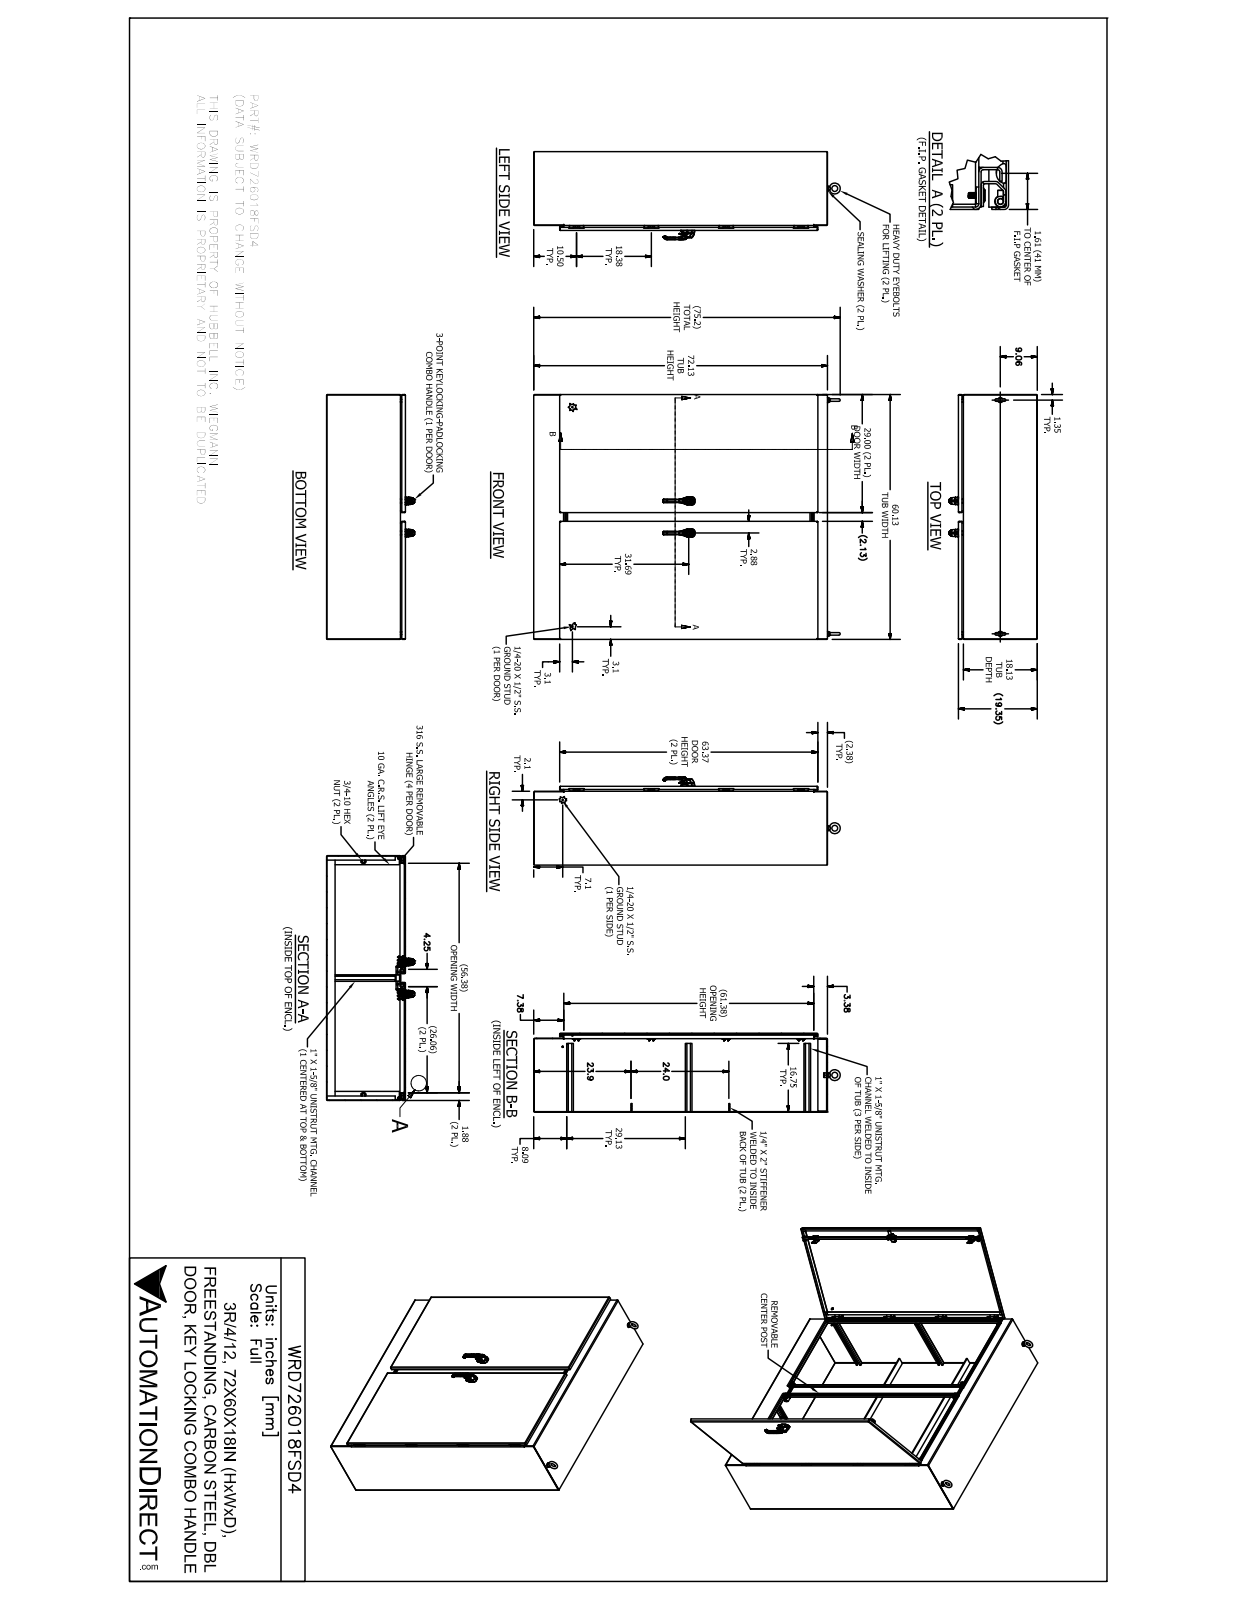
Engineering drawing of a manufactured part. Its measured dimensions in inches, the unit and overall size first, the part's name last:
Units: inches
Overall size (bounding box): 75.248 × 60.133 × 21.527
Round holes (diameter × count): ⌀0.266 ×20, ⌀0.23 ×16, ⌀0.281 ×16, ⌀0.65 ×16, ⌀0.2 ×8, ⌀0.277 ×8, ⌀0.281 ×6, ⌀0.156 ×4, ⌀0.252 ×4, ⌀0.4 ×4, ⌀0.45 ×4, ⌀0.241 ×3
Round bosses / shafts (diameter × count): ⌀0.625 ×15, ⌀0.25 ×13, ⌀0.533 ×4, ⌀0.438 ×4, ⌀0.375 ×4, ⌀0.313 ×4, ⌀0.213 ×4, ⌀1 ×3
Partial cylindrical surfaces — rounded edges, fillets, slot ends (radius × count): R0.062 ×43, R0.05 ×32, R0.125 ×32, R0.063 ×17, R0.01 ×16, R0.019 ×16, R0.025 ×16, R0.053 ×16
Main face-to-face distances: 0.104, 19.245, 19.141, 19.349, 60.021, 72.021, 18.021, 1.224, 59.917, 60.125
Hole centre spacings: 1, 18.375, 36.75, 61.676, 18.375, 58.875, 58.884, 61.676
Volume: 1 847 in³ · Surface area: 33 441 in²
Bodies: 155 solids, 3276 faces (1520 planar, 1096 cylindrical, 660 other)
Part name (STEP PRODUCT): WRD726018FSD4
STEP written by: SolidWorks 2017 (AUTOMOTIVE_DESIGN)
